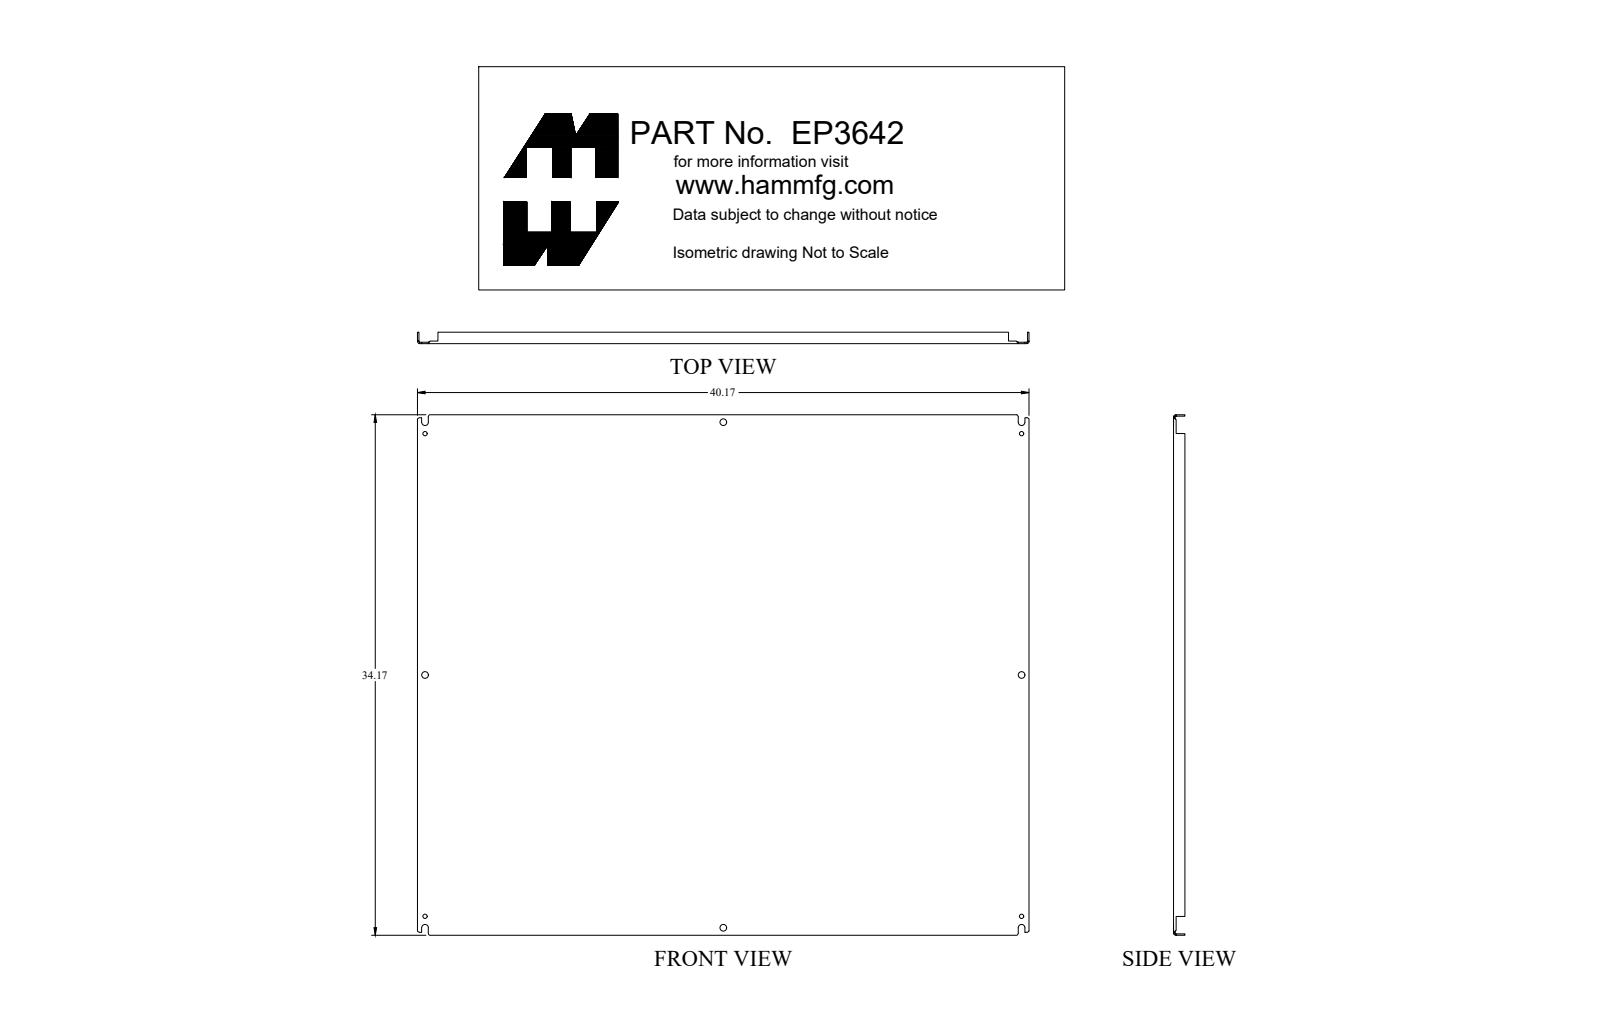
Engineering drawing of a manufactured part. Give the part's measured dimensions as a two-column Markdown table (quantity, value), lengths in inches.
| quantity | value |
| --- | --- |
| part name | EP3642 |
| STEP written by | SolidWorks 2018 (AUTOMOTIVE_DESIGN) |
| units | inches |
| bodies | 1 solid, 136 faces (74 planar, 46 cylindrical, 16 other) |
| overall size | 40.17 × 34.17 × 0.75 |
| volume | 138.3 in³ |
| surface area | 2 926 in² |
| round holes (diameter × count) | 0.281 × 4, 0.437 × 4 |
| partial cylindrical surfaces (radius × count) | 0.048 × 4, 0.063 × 4, 0.143 × 4, 0.219 × 4 |
| main face-to-face distances | 0.095, 34.075, 40.075, 34.17, 33.98, 39.98, 40.17, 0.75, 0.655, 0.171 |
| hole center spacings | 15.844, 19.608, 25.677, 37.897, 42.27, 39.188, 31.688, 50.397 |
